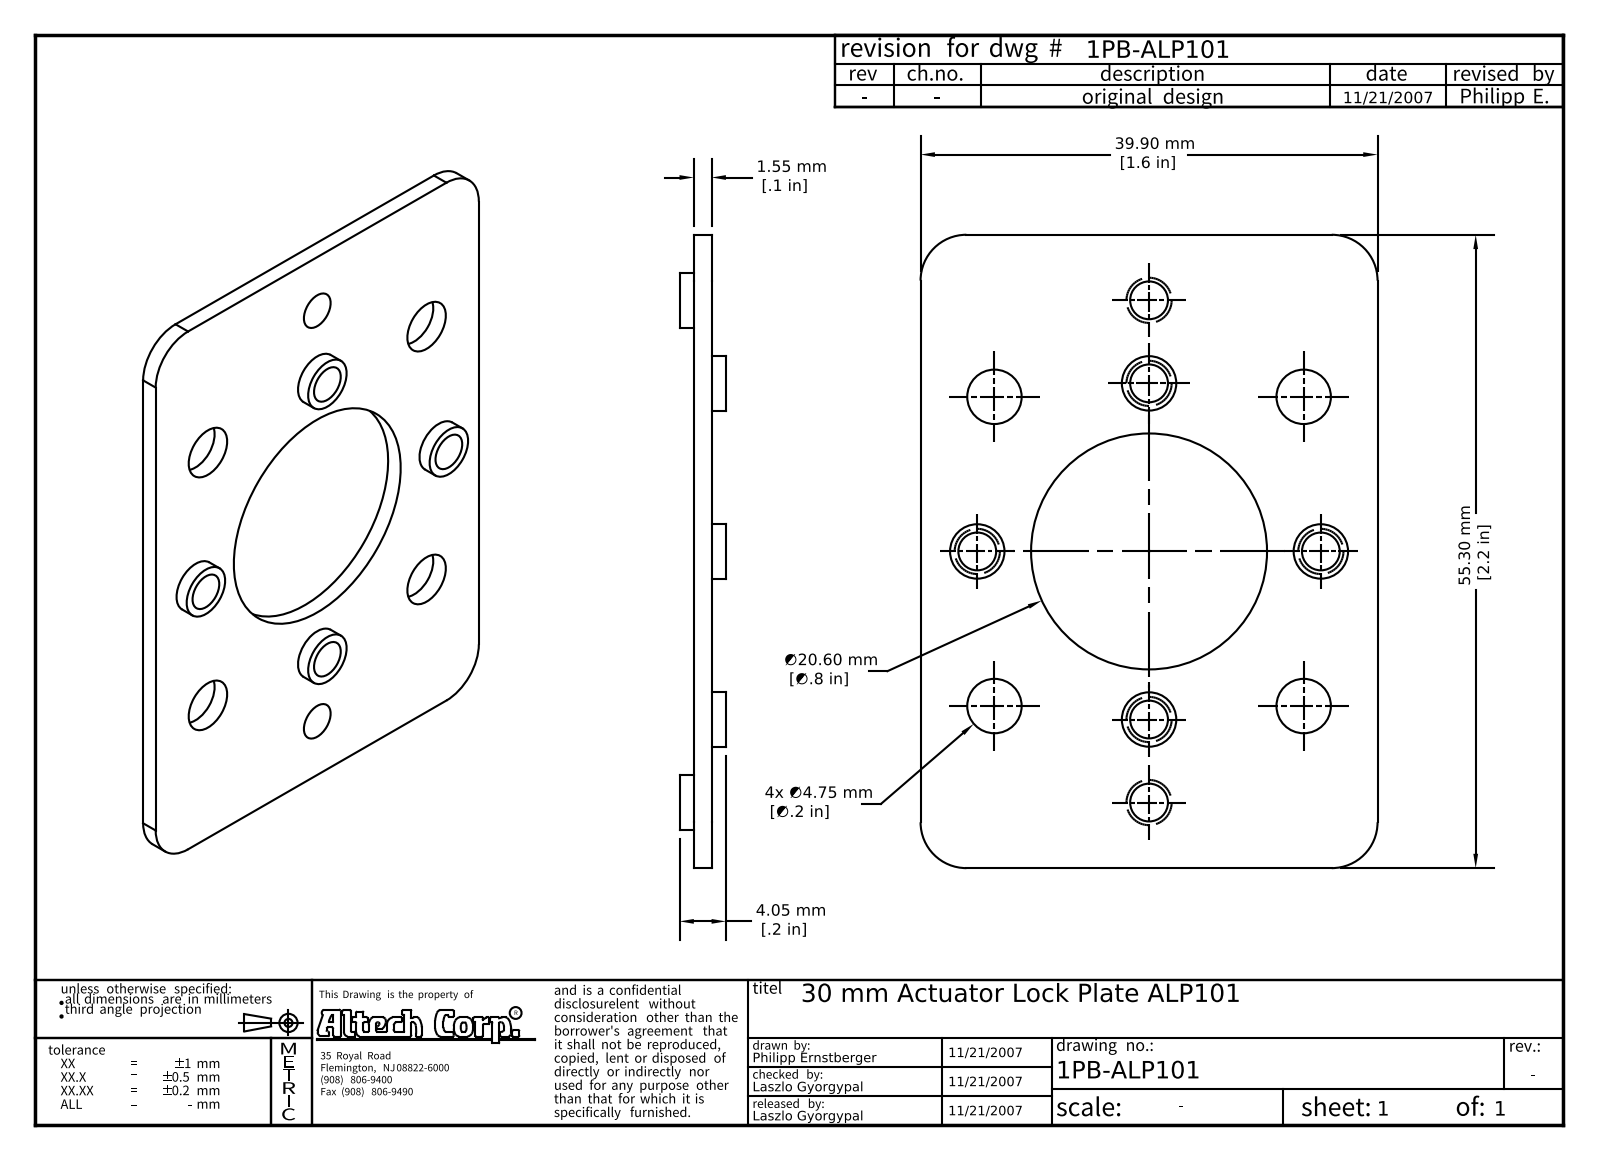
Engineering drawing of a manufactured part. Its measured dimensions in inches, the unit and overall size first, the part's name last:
Units: inches
Overall size (bounding box): 2.177 × 1.571 × 0.159
Round holes (diameter × count): ⌀0.13 ×6, ⌀0.187 ×4, ⌀0.811 ×1
Round bosses / shafts (diameter × count): ⌀0.187 ×6
Partial cylindrical surfaces — rounded edges, fillets, slot ends (radius × count): R0.157 ×4
Main face-to-face distances: 0.061, 1.571, 0.049, 0.11, 2.177, 0.159
Hole centre spacings: 0.533, 0.535, 0.752, 1.063, 1.242, 1.493, 0.285, 0.591
Volume: 0.168 in³ · Surface area: 6.569 in²
Bodies: 1 solid, 33 faces (12 planar, 21 cylindrical, 0 other)
Part name (STEP PRODUCT): ALP101
STEP written by: Autodesk Inventor 2008 (AUTOMOTIVE_DESIGN)
